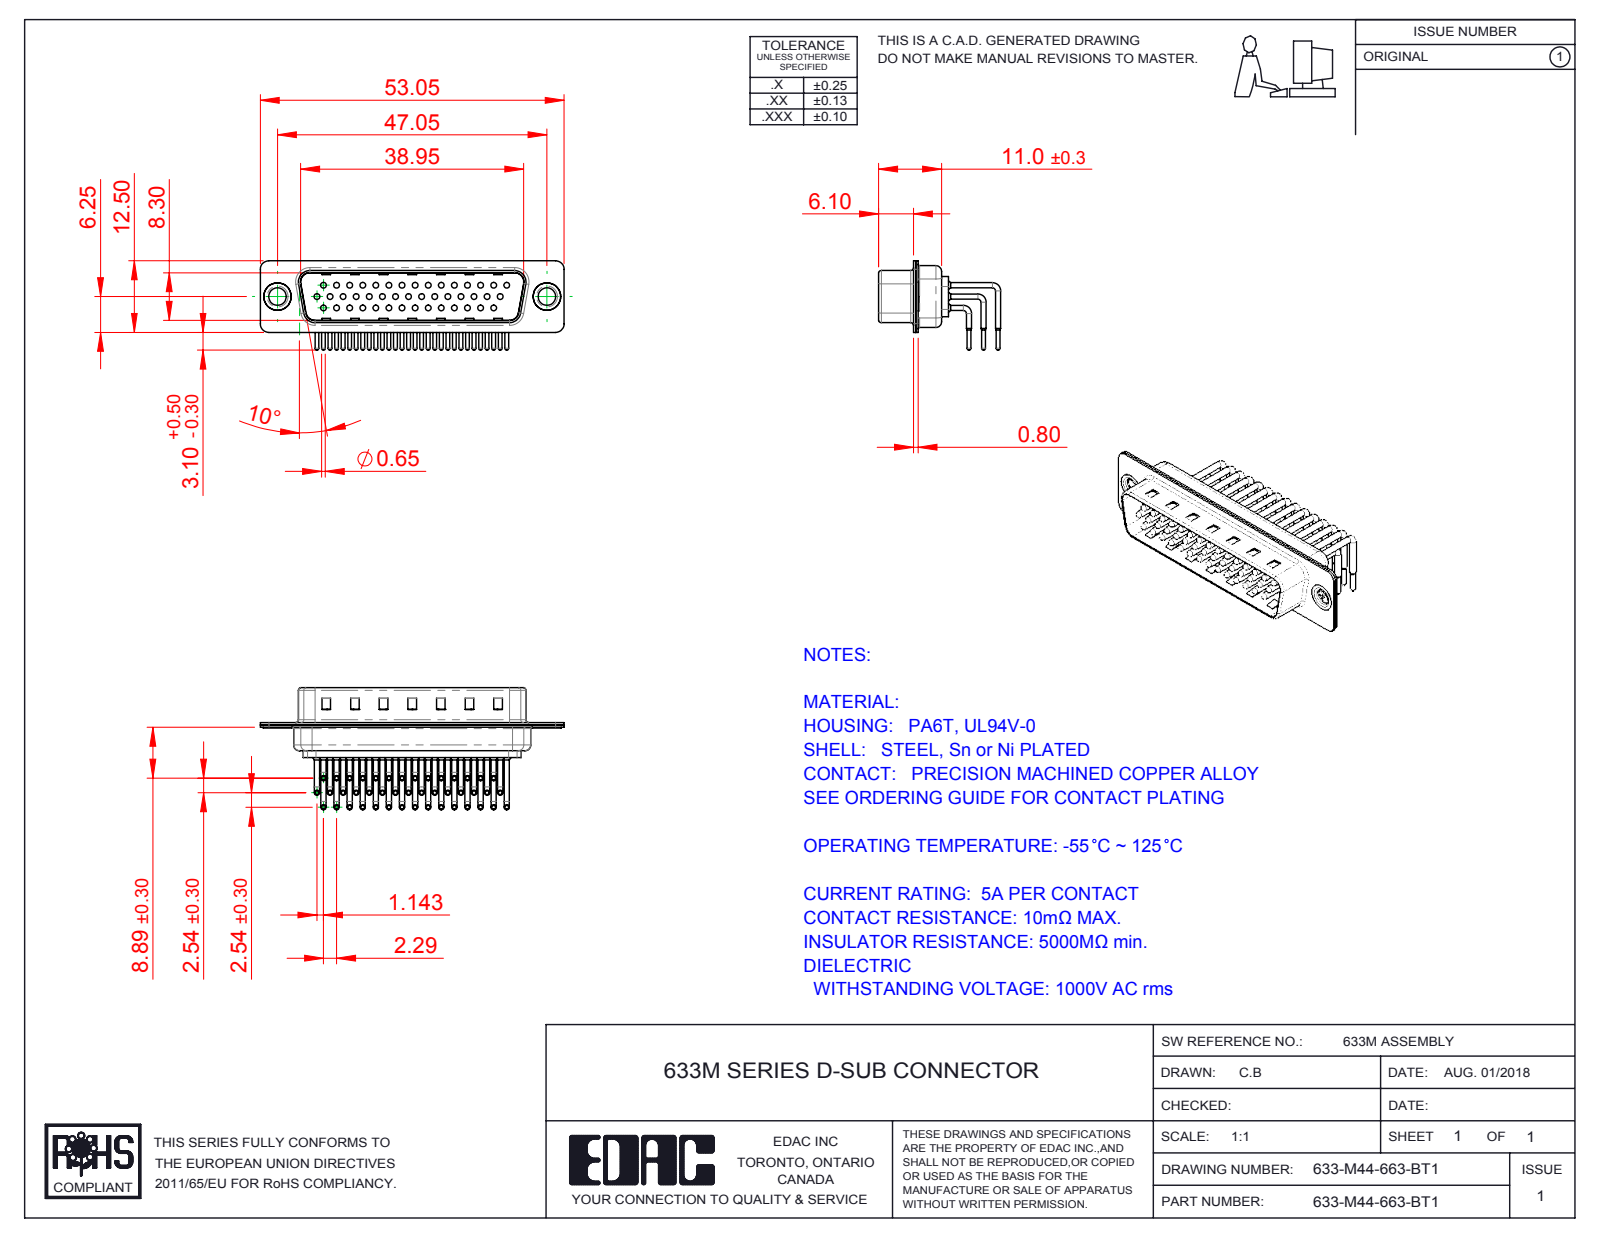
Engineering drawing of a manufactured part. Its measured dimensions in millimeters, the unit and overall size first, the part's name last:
Units: millimetres
Overall size (bounding box): 53.05 × 21.32 × 15.6
Round holes (diameter × count): ⌀1 ×44, ⌀1.7 ×44, ⌀2 ×44, ⌀3.05 ×2, ⌀4 ×2, ⌀4.8 ×2
Round bosses / shafts (diameter × count): ⌀0.9 ×88, ⌀1.5 ×44, ⌀0.65 ×44, ⌀5 ×2, ⌀4.9 ×2, ⌀3.55 ×2, ⌀1 ×2
Partial cylindrical surfaces — rounded edges, fillets, slot ends (radius × count): R1.01 ×44, R1.5 ×16, R2 ×12, R0.5 ×8, R1.6 ×8, R0.25 ×4, R0.6 ×4, R0.65 ×4
Main face-to-face distances: 0.4, 0.85, 9.55, 1.5, 8.7, 1.9, 1.25, 10.4, 0.35, 9.15
Hole centre spacings: 2.28, 3.96, 2.29, 4.57, 8.24, 6.86, 11.43, 12.72
Volume: 3 057 mm³ · Surface area: 9 906 mm²
Bodies: 49 solids, 5190 faces (2987 planar, 1705 cylindrical, 498 other)
Part name (STEP PRODUCT): 633M Thru Hole Rivet; 633M Contact Row 3; 633M Shell Rear_44 Contacts; 633M Shell Front_44 Contacts (+4 more)
STEP written by: SolidWorks 2016 (CONFIG_CONTROL_DESIGN)
